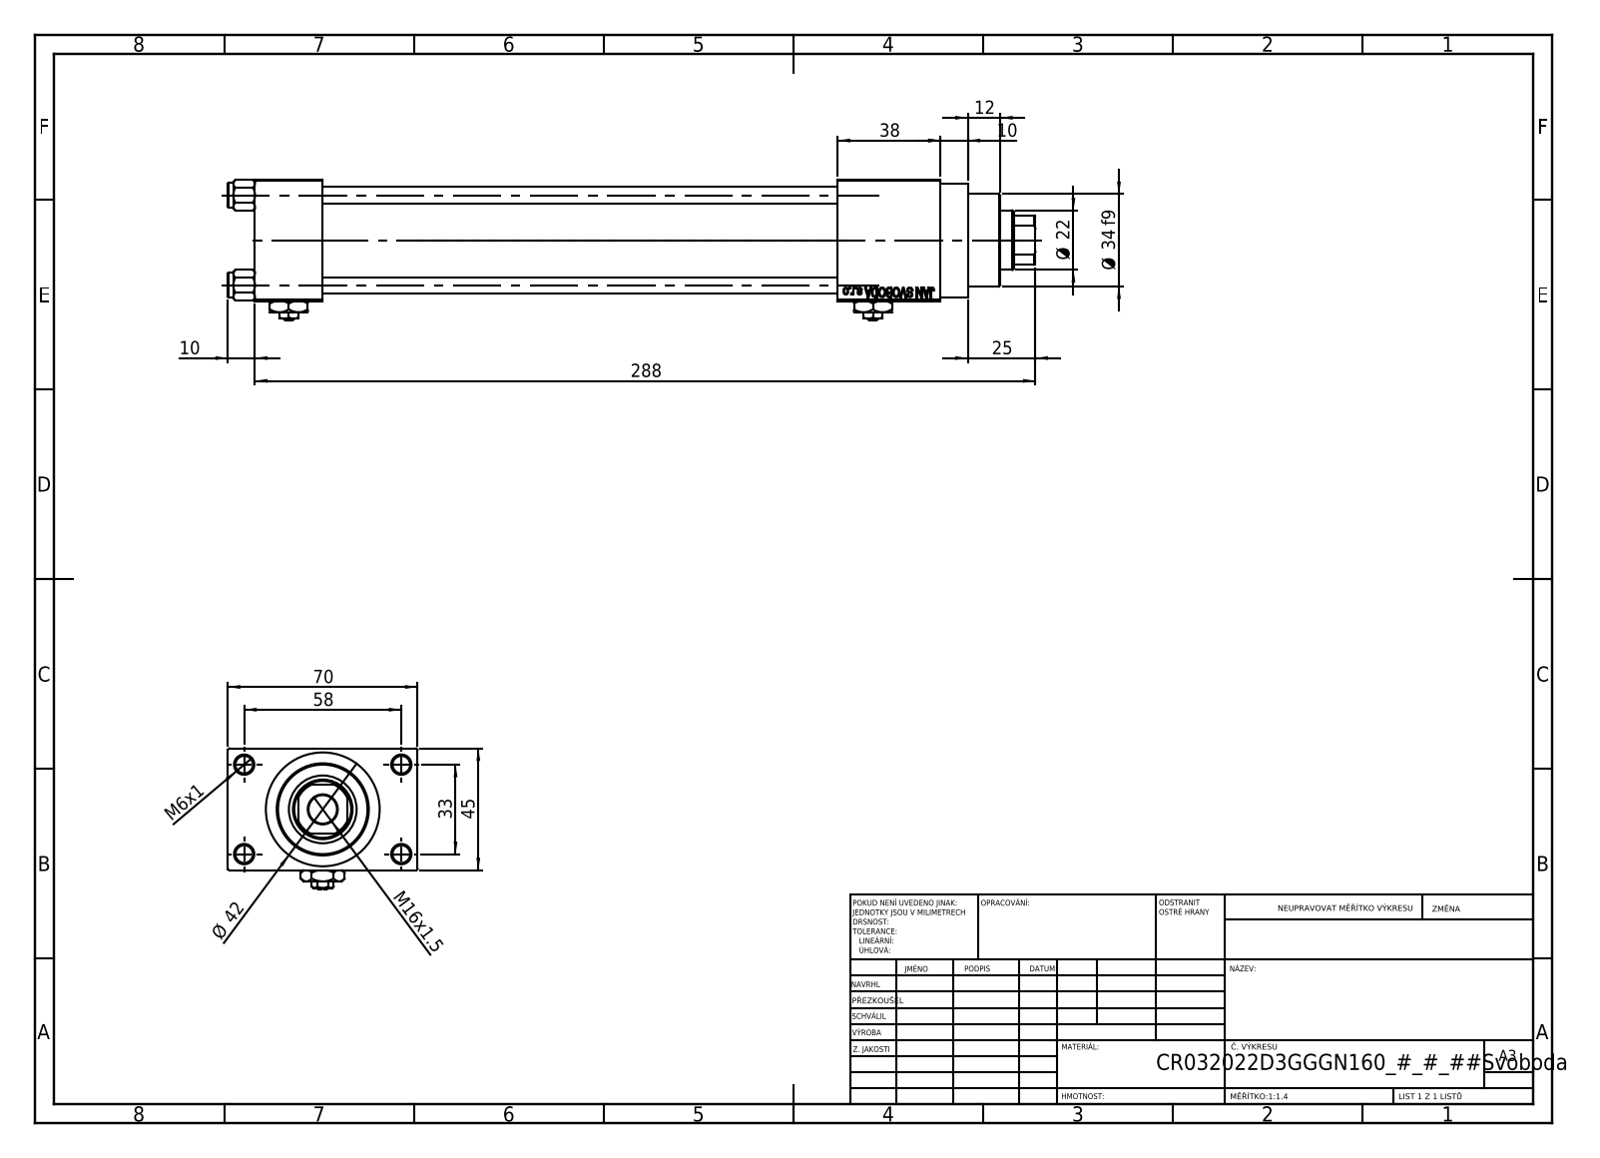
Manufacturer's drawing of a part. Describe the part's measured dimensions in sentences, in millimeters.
The part is named "V215CR_D_Body; V215CR_VCP_D; V215CR_D_TYCINKA; V215_VC_A (+2 more)". Its 3-D file was written by "SolidWorks 2019 (CONFIG_CONTROL_DESIGN)". It is 13 solids with 1202 faces: 542 planar, 100 cylindrical and 560 other. Overall it measures 298 by 70 by 52 millimeters. Its volume is 358 601 cubic millimeters and its surface area 132 220 square millimeters. Round holes: 4 of diameter 6, 4 of diameter 6.5, 2 of diameter 7, 2 of diameter 13.16, 2 of diameter 20, 1 of diameter 10.5, 1 of diameter 22, 1 of diameter 24, 1 of diameter 25, 1 of diameter 32, 1 of diameter 33. Round bosses or shafts: 4 of diameter 9, 1 of diameter 42, 1 of diameter 38, 1 of diameter 34. Partial cylindrical surfaces (rounded edges, fillets, slot ends): 1 of radius 10.5. The main face-to-face distances are 45, 25, 12.5, 57.5, 190, 215, 228, 38, 70, 253. The hole center spacings are 12.4, 23.48, 33.2, 33.37, 35.35, 45.6, 56.35, 33.
